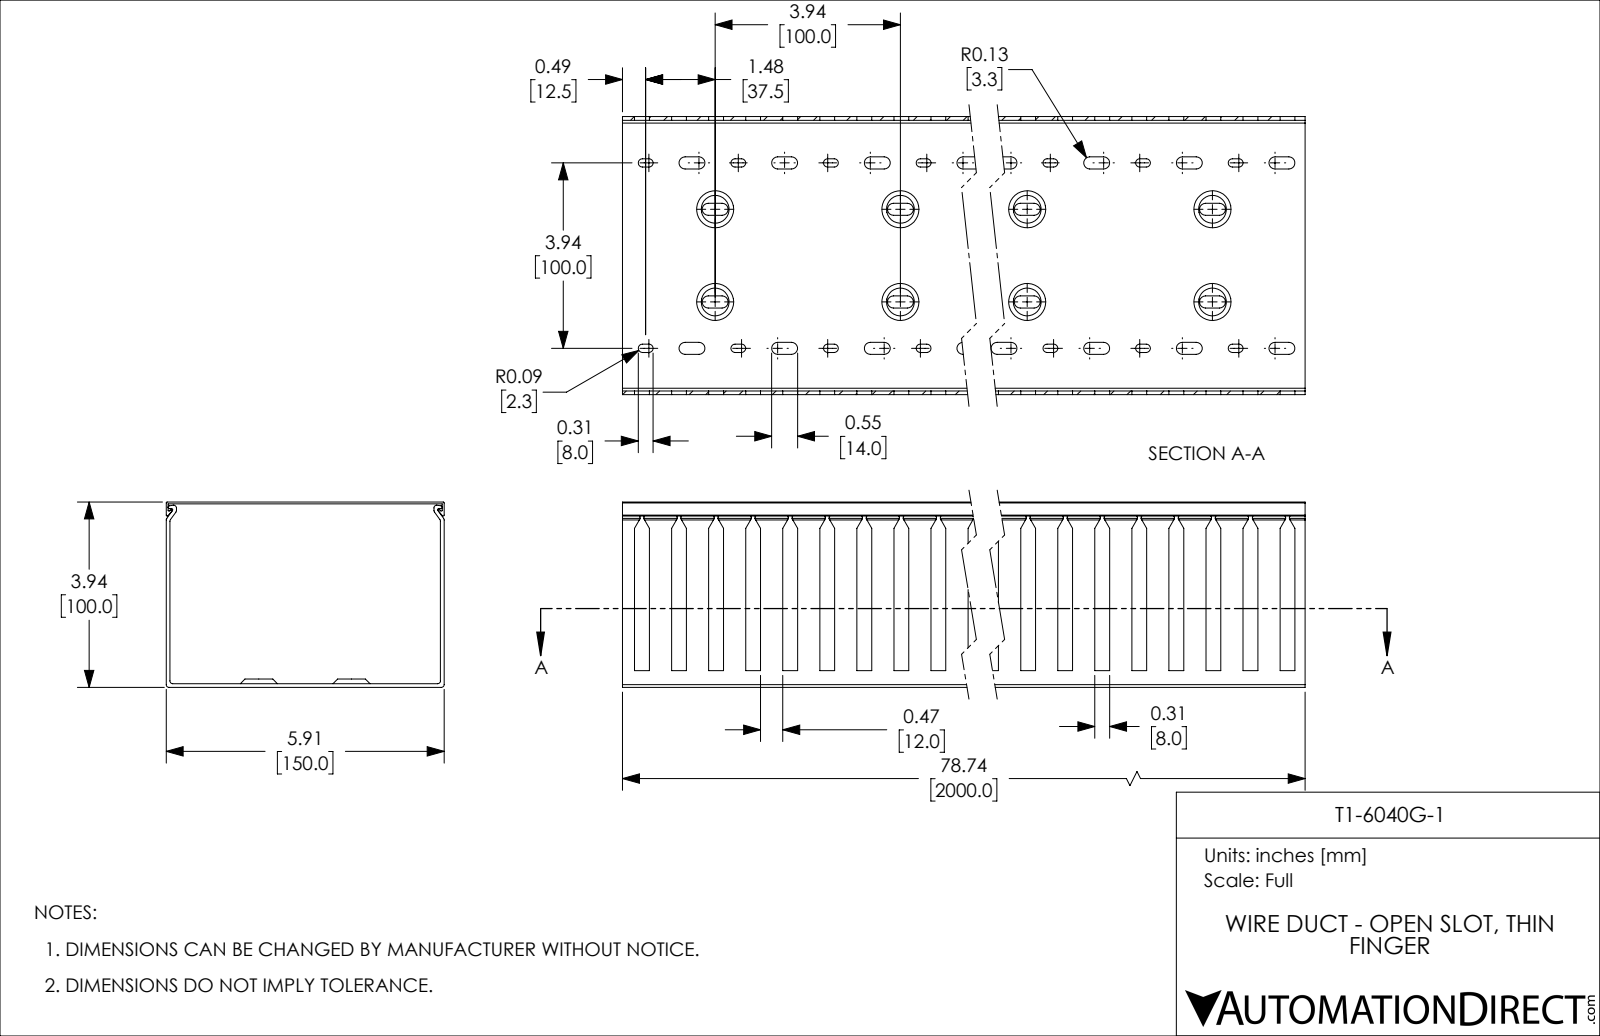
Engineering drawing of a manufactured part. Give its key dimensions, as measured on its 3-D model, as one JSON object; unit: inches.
{"part_name": "T1-6040W-1", "step_written_by": "SolidWorks 2021 (CONFIG_CONTROL_DESIGN)", "units": "inches", "bodies": {"solids": 2, "faces": 1661, "planar": 790, "cylindrical": 791, "other": 80}, "overall_size": [78.74, 5.906, 3.937], "volume_in3": 103.4, "surface_area_in2": 3159, "partial_cylinders_radius": [[0.128, 240], [0.089, 160], [0.059, 12], [0.02, 8], [0.03, 6]], "face_to_face_distances": [0.079, 5.827, 0.039, 3.937, 3.898, 3.819, 3.858, 5.906, 5.748, 5.866]}
